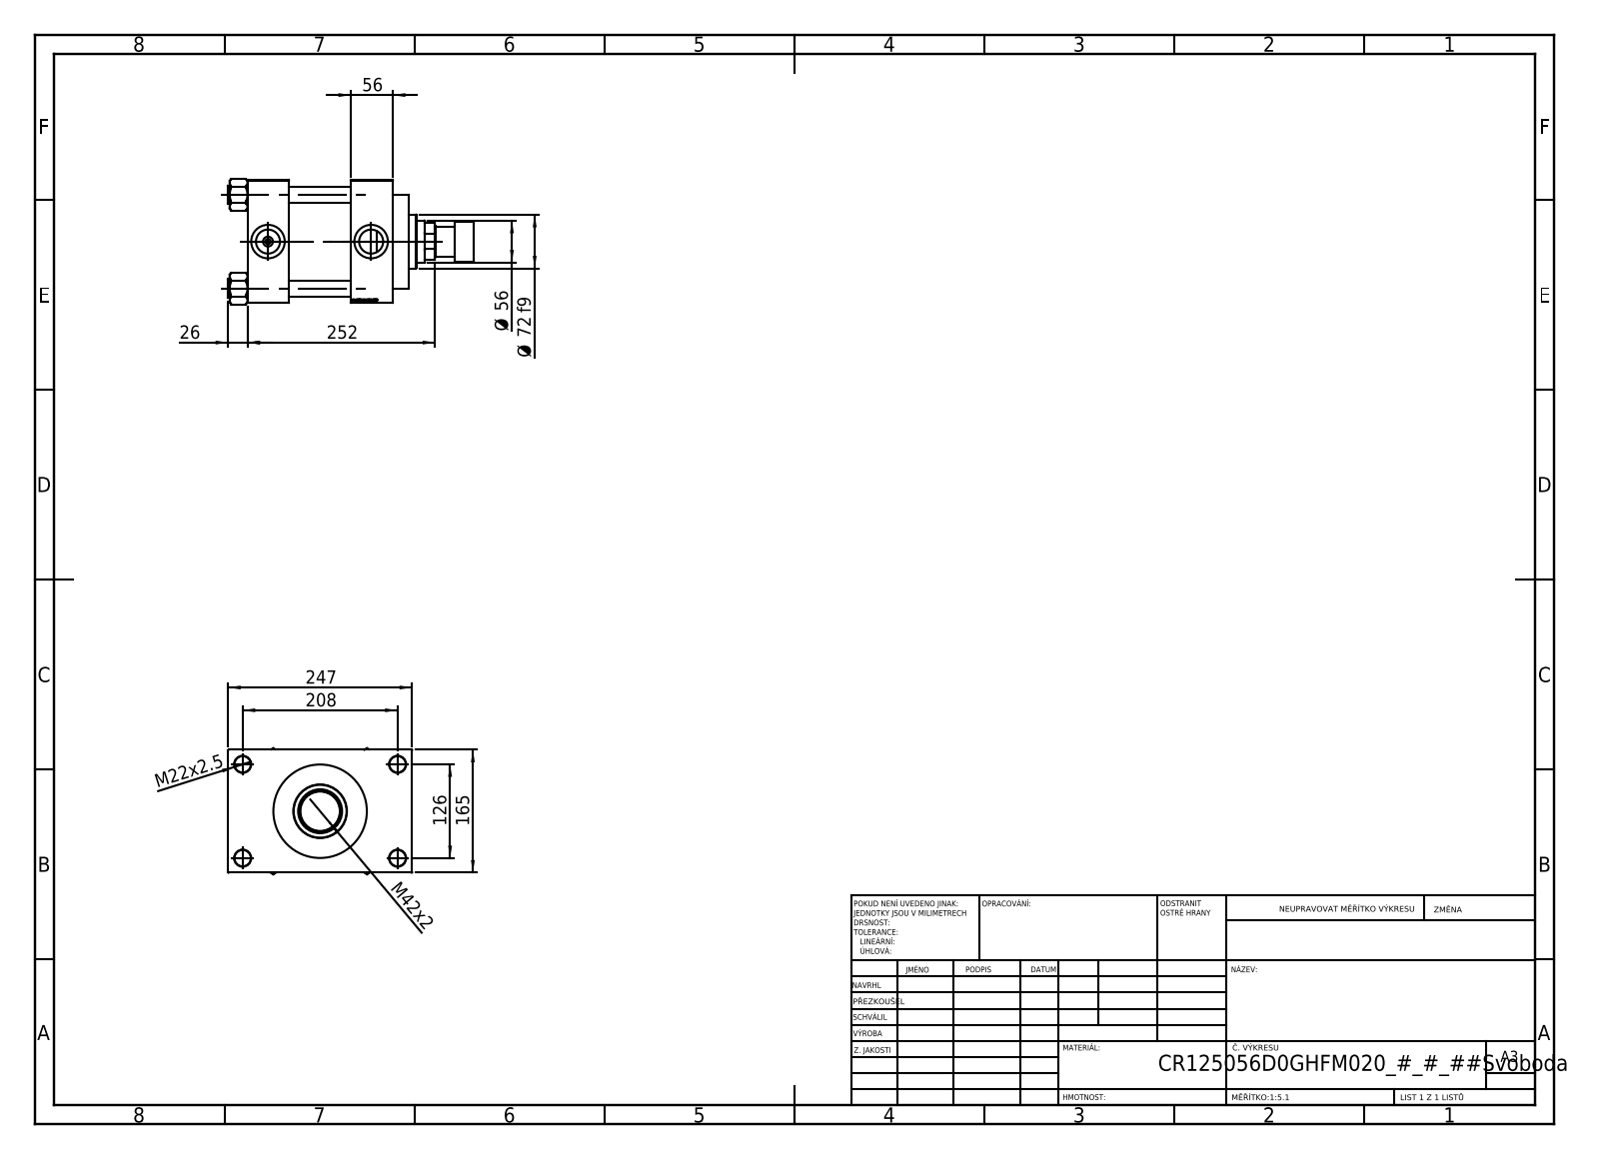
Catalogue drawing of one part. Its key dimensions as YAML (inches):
part_name: "NUT_M5_D; V215CR_ROD_END_F; V215CR_D_TYCINKA; V215CR_VCP_D (+2 more)"
step_written_by: "SolidWorks 2019 (CONFIG_CONTROL_DESIGN)"
units: inches
bodies: {solids: 12, faces: 1162, planar: 548, cylindrical: 90, other: 524}
overall_size: [12.992, 9.724, 6.659]
volume: 306.2
surface_area: 847.2
round_holes:
  - {diameter: 0.866, count: 8}
  - {diameter: 0.276, count: 2}
  - {diameter: 1.269, count: 2}
  - {diameter: 1.772, count: 2}
  - {diameter: 1.594, count: 1}
  - {diameter: 2.205, count: 1}
  - {diameter: 2.323, count: 1}
  - {diameter: 3.78, count: 1}
  - {diameter: 4.921, count: 1}
  - {diameter: 4.941, count: 1}
round_bosses_or_shafts:
  - {diameter: 0.984, count: 4}
  - {diameter: 5.157, count: 1}
  - {diameter: 2.835, count: 1}
  - {diameter: 2.126, count: 1}
  - {diameter: 1.575, count: 1}
face_to_face_distances: [6.496, 5.472, 3.307, 2.165, 2.205, 7.677, 5.512, 1.614, 8.11, 6.84]
hole_center_spacings: [1.616, 3.505, 4.787, 4.957, 5.215, 6.573, 8.233, 4.961]
